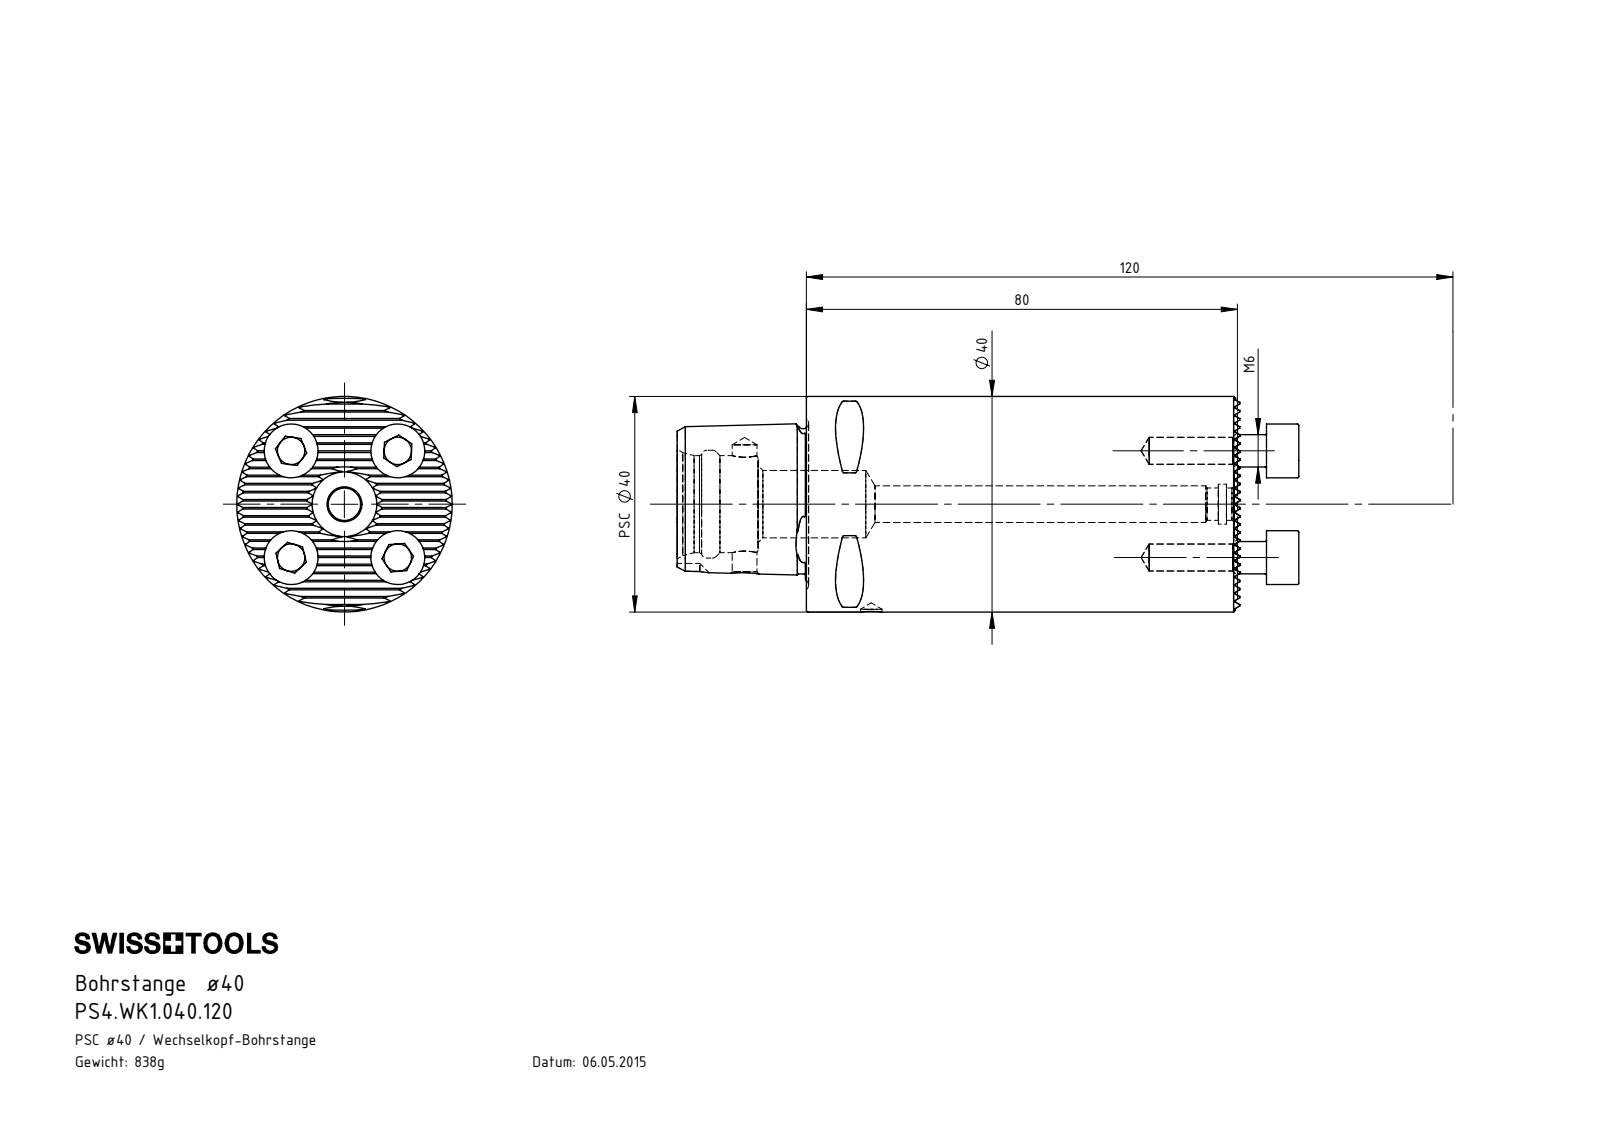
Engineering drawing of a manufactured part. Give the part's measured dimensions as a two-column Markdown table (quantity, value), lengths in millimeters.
| quantity | value |
| --- | --- |
| part name | PS4.WK1.040.120; DIN 3771 - 6x1; ISO 4762 - M6 x 16; PS4-WK1.040.120_B |
| STEP written by | SolidWorks 2017 (AUTOMOTIVE_DESIGN) |
| units | millimeters |
| bodies | 6 solids, 490 faces (241 planar, 109 cylindrical, 140 other) |
| overall size | 115.4 × 40 × 40 |
| volume | 106 684 mm³ |
| surface area | 22 212 mm² |
| round holes (diameter × count) | 5 × 4, 4 × 1, 4.6 × 1, 6 × 1, 6.8 × 1, 7.4 × 1, 12.5 × 1, 18 × 1, 20 × 1 |
| round bosses / shafts (diameter × count) | 10 × 4, 6 × 4, 40 × 1 |
| partial cylindrical surfaces (radius × count) | 0.12 × 27, 0.3 × 8, 3 × 1 |
| main face-to-face distances | 1.3, 2.6, 3.9, 5.2, 12.99, 9.09, 11.69, 7.79, 10.39, 6.5 |
| hole center spacings | 14, 19.8, 28, 23.5 |
